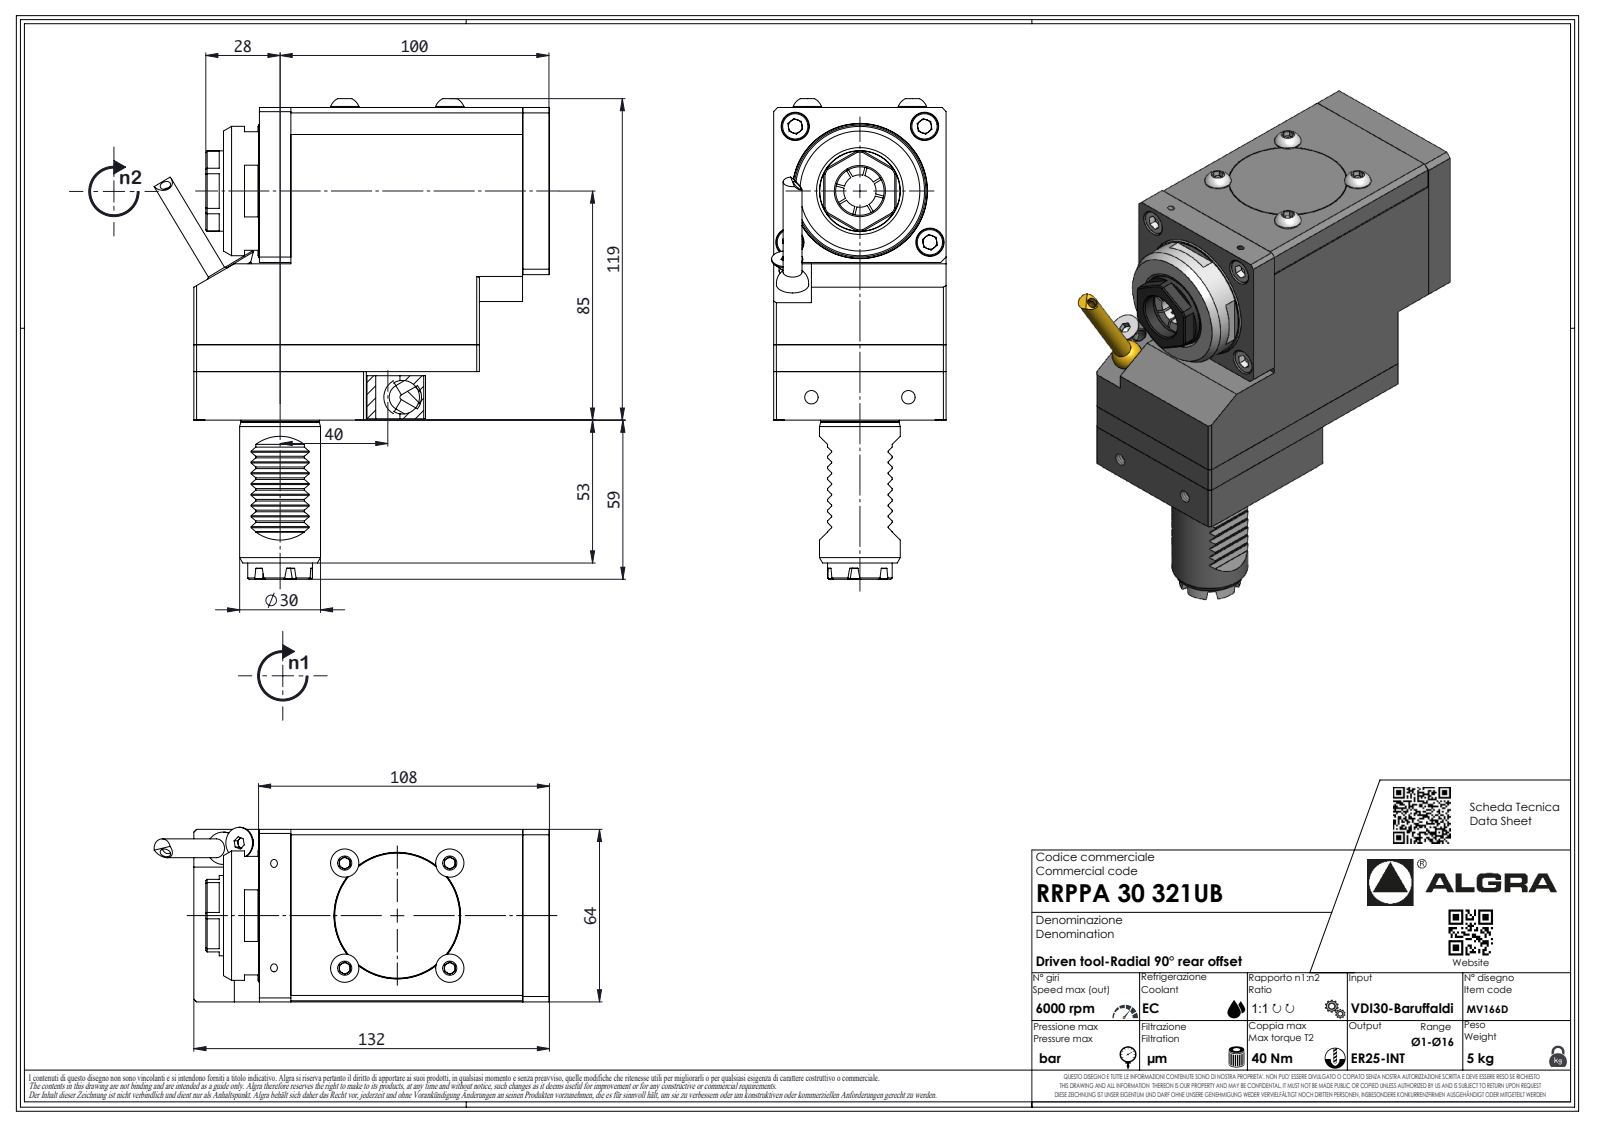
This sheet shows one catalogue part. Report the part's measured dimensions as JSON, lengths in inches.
{"part_name": "RRPPA30321UB", "step_written_by": "SolidWorks 2023 (AUTOMOTIVE_DESIGN)", "units": "inches", "bodies": {"solids": 1, "faces": 598, "planar": 393, "cylindrical": 87, "other": 118}, "overall_size": [6.892, 5.861, 2.52], "volume_in3": 51.2, "surface_area_in2": 116.6, "round_holes": [[0.083, 1], [0.157, 1], [1.504, 1], [1.661, 1], [1.819, 1], [1.976, 1]], "round_bosses_or_shafts": [[1.969, 1], [1.89, 1], [1.811, 1], [1.654, 1], [1.496, 1], [1.339, 1], [1.181, 1], [1.173, 1]], "partial_cylinders_radius": [[0.012, 16], [0.013, 7], [0.02, 7], [0.146, 7], [0.008, 6], [0.008, 1], [0.079, 1], [0.299, 1]], "face_to_face_distances": [2.52, 4.567, 2.283, 5.28, 3.858, 0.709, 4.173, 1.106, 4.321, 3.215]}
